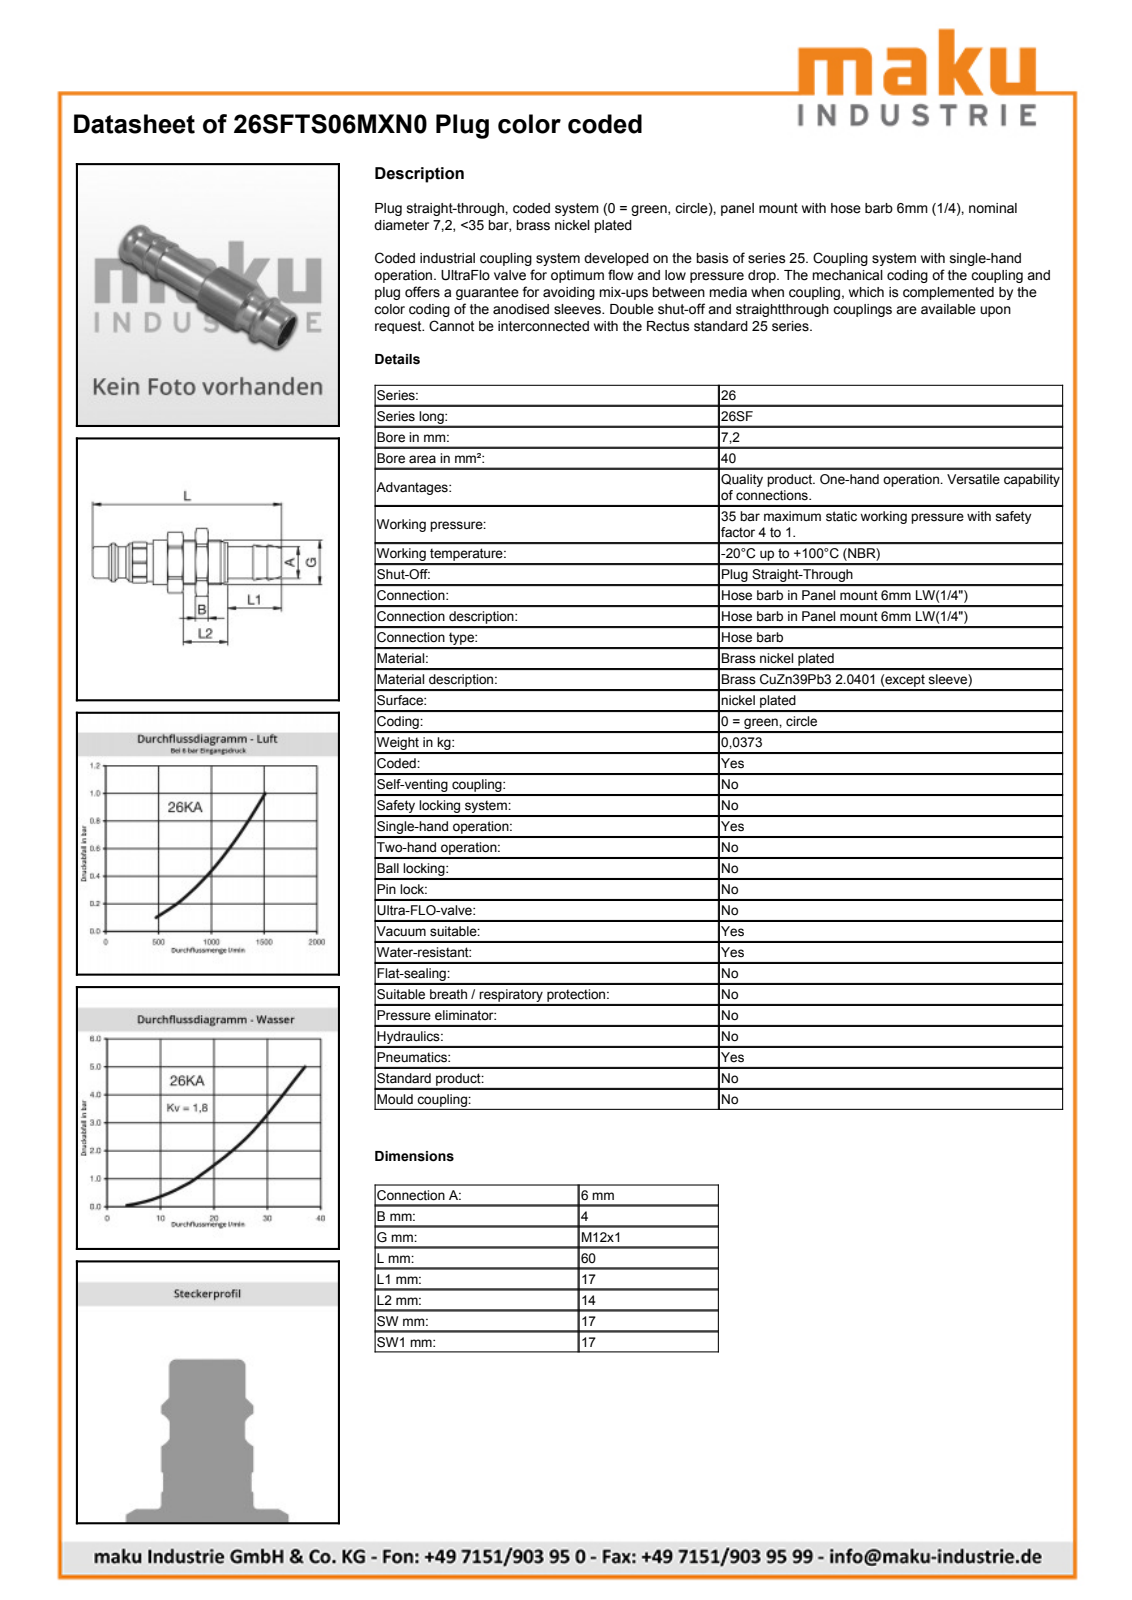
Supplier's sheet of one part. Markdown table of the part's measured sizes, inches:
| quantity | value |
| --- | --- |
| part name | D113126; D113127; D113125; D104664 |
| STEP written by | Autodesk Inventor 2013 (AUTOMOTIVE_DESIGN) |
| units | inches |
| bodies | 3 solids, 94 faces (25 planar, 27 cylindrical, 42 other) |
| overall size | 2.362 × 0.754 × 0.702 |
| volume | 0.275 in³ |
| surface area | 7.404 in² |
| round holes (diameter × count) | 0.157 × 1, 0.309 × 1, 0.545 × 1, 0.553 × 1 |
| round bosses / shafts (diameter × count) | 0.61 × 1, 0.551 × 1, 0.492 × 1, 0.472 × 1, 0.417 × 1, 0.394 × 1, 0.384 × 1, 0.24 × 1 |
| partial cylindrical surfaces (radius × count) | 0.377 × 1 |
| main face-to-face distances | 0.669, 0.191, 0.157, 0.348, 0.565, 0.407, 0.217, 0.177, 0.203, 0.361 |
